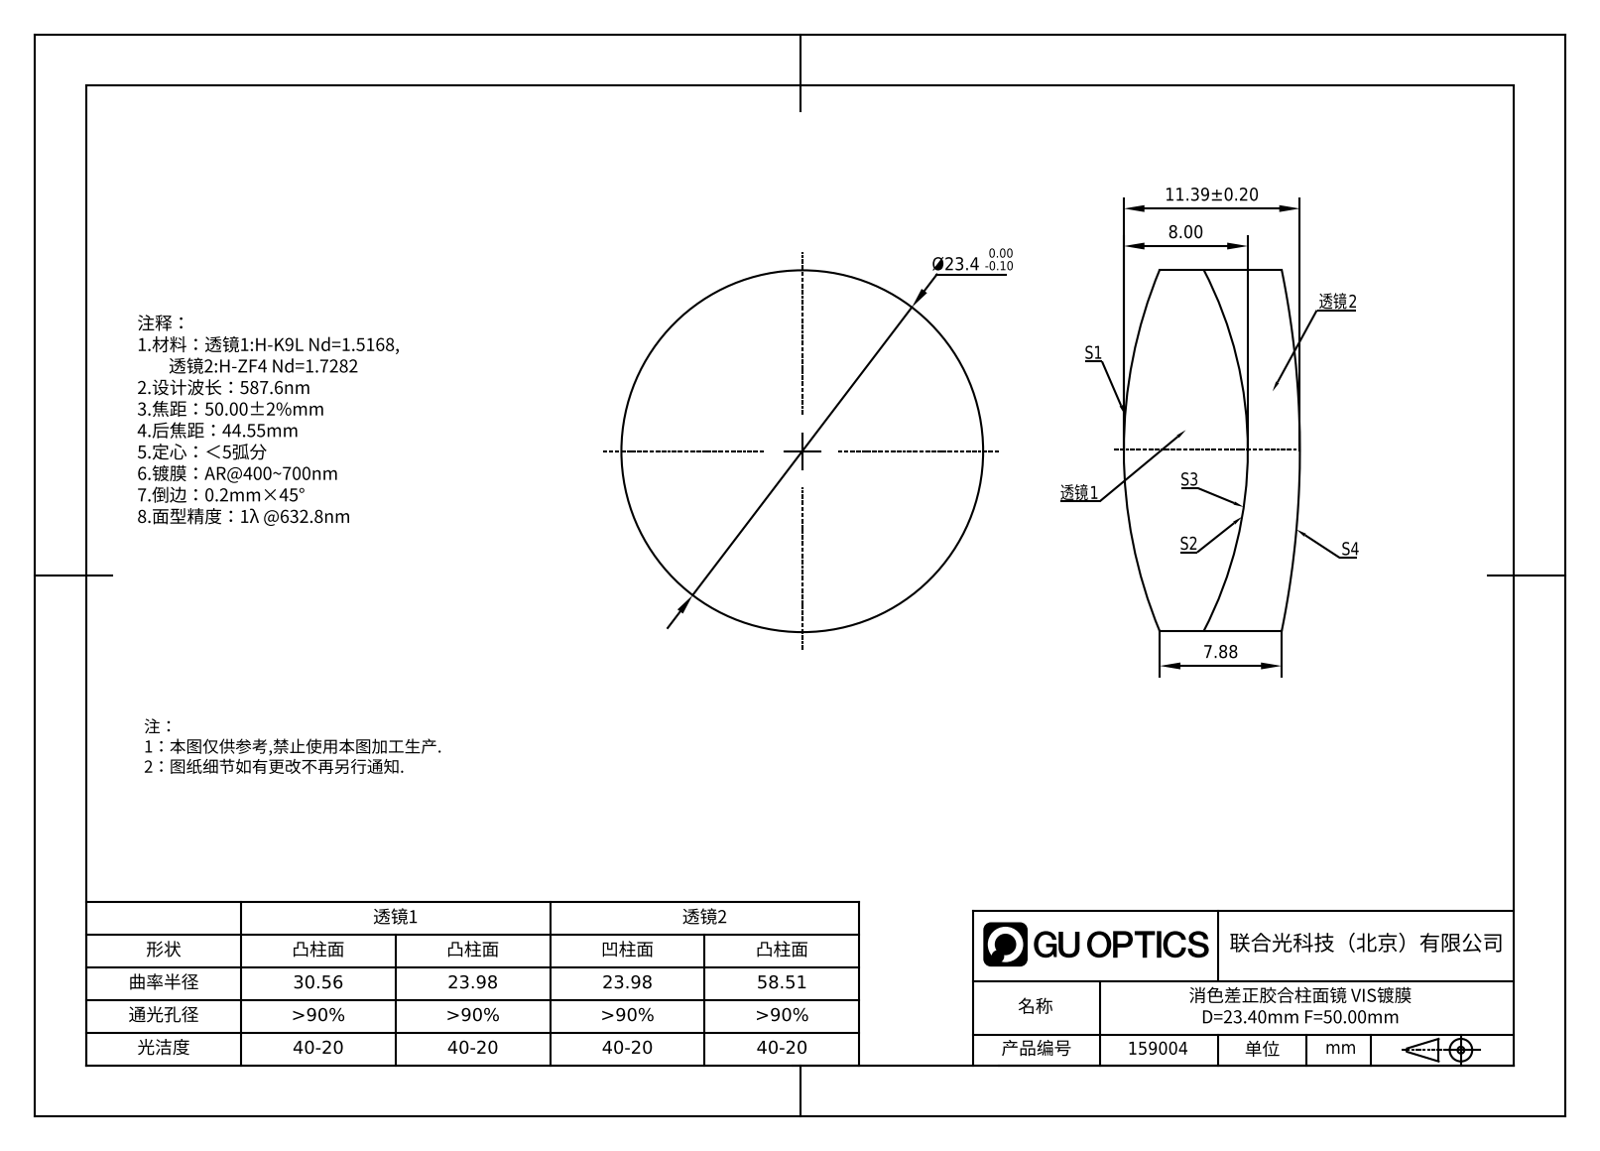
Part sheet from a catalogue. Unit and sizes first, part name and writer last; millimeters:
Units: millimetres
Overall size (bounding box): 23.4 × 23.4 × 11.39
Round bosses / shafts (diameter × count): ⌀23.4 ×1
Partial cylindrical surfaces — rounded edges, fillets, slot ends (radius × count): R30.56 ×1, R58.51 ×1
Volume: 4 526 mm³ · Surface area: 1 580 mm²
Bodies: 1 solid, 5 faces (0 planar, 5 cylindrical, 0 other)
Part name (STEP PRODUCT): 159004
STEP written by: SolidWorks 2020 (CONFIG_CONTROL_DESIGN)
